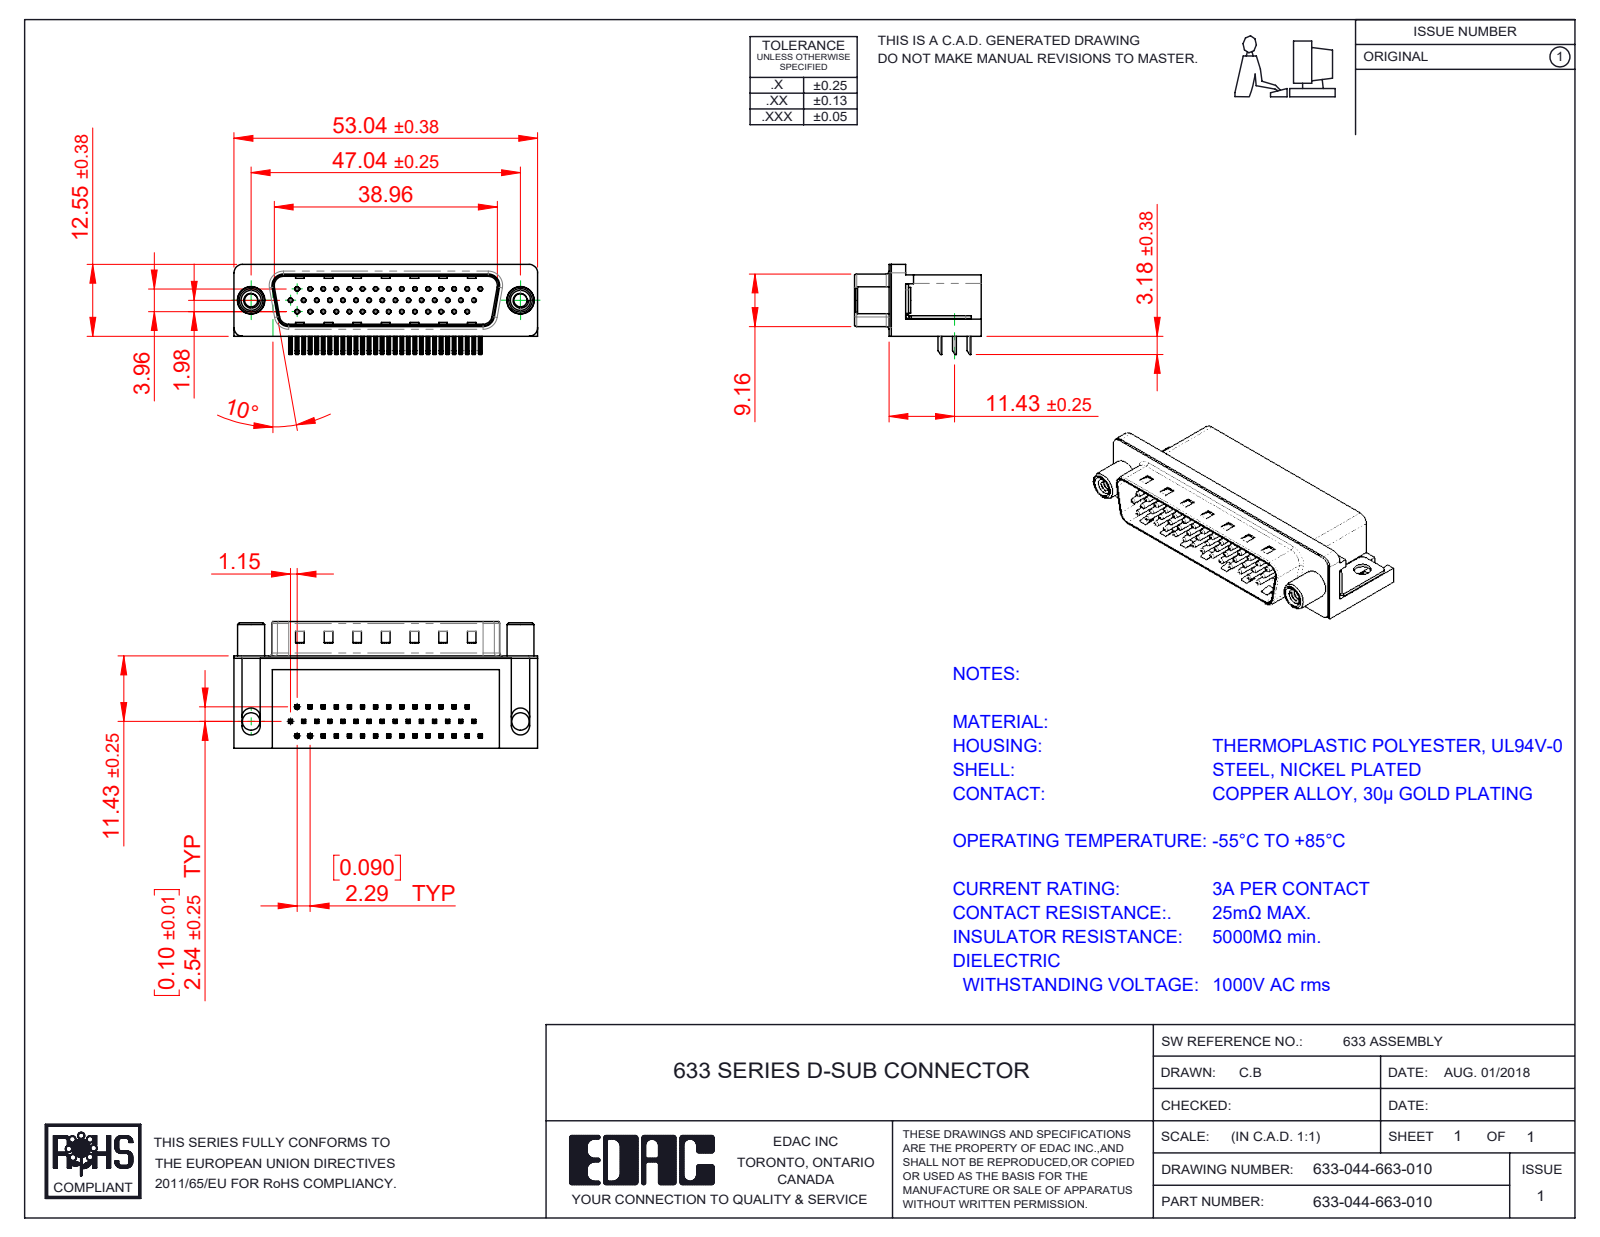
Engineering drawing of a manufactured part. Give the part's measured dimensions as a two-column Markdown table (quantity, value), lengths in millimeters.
| quantity | value |
| --- | --- |
| part name | 633 Housing_44 Contact; 633-044-663-010; 633 Round Threaded Standoff; 633 Contact Bottom (+4 more) |
| STEP written by | SolidWorks 2016 (CONFIG_CONTROL_DESIGN) |
| units | millimeters |
| bodies | 50 solids, 3682 faces (2307 planar, 1068 cylindrical, 307 other) |
| overall size | 53.04 × 22.1 × 15.73 |
| volume | 8 203 mm³ |
| surface area | 10 405 mm² |
| round holes (diameter × count) | 0.35 × 44, 0.8 × 44, 2.3 × 2, 3.05 × 2, 3.1 × 2, 4 × 2, 4.8 × 2, 5 × 2 |
| round bosses / shafts (diameter × count) | 0.75 × 44, 4.9 × 2, 4.7 × 2, 4.5 × 2, 3.85 × 2 |
| partial cylindrical surfaces (radius × count) | 0.25 × 176, 0.12 × 88, 1 × 16, 0.5 × 9, 1.6 × 8, 1.5 × 7, 0.9 × 4, 2 × 4 |
| main face-to-face distances | 0.4, 10.35, 15.7, 2.9, 8.76, 2.5, 2.1, 2.54, 16.1, 10.7 |
| hole center spacings | 2.29, 4.57, 4.58, 2.28, 6.87, 9.16, 11.45, 2.27 |
